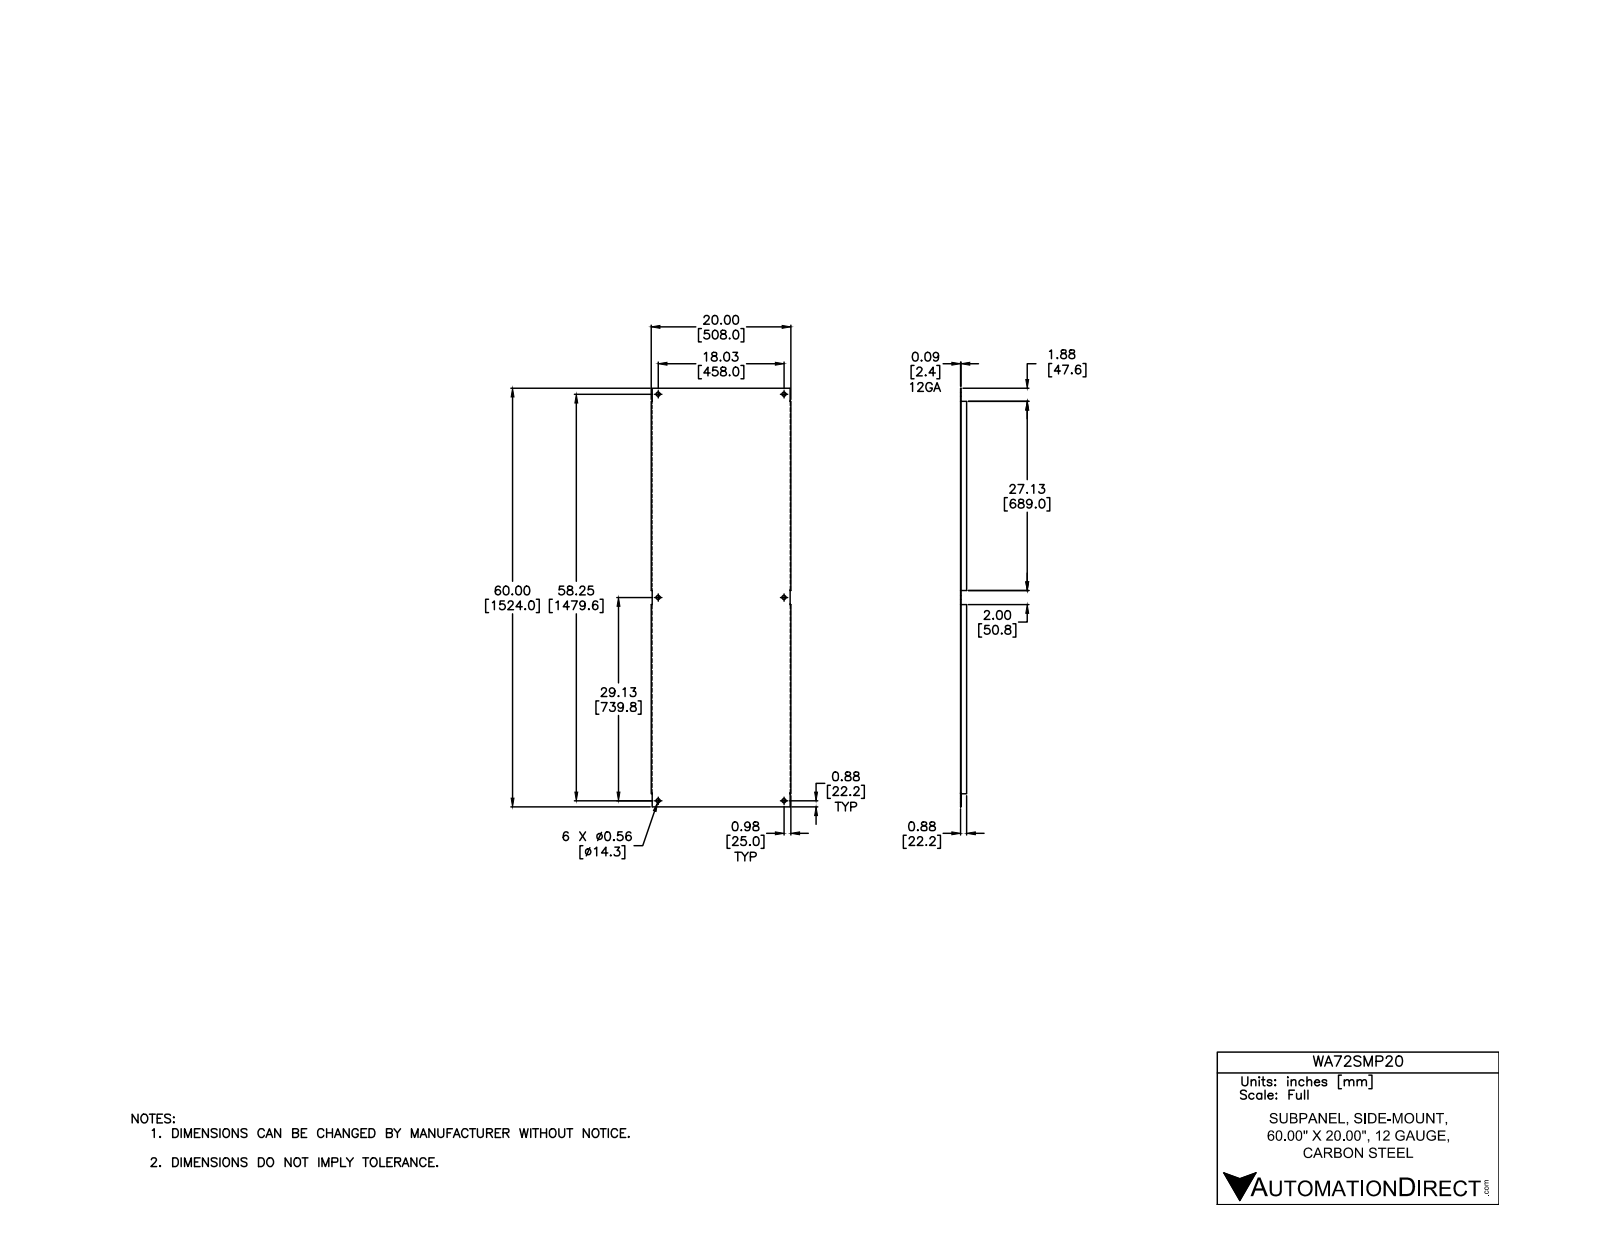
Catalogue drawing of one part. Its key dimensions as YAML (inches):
part_name: "WA60SMP14-WA90SMP20"
step_written_by: "Autodesk Inventor 2012 (AUTOMOTIVE_DESIGN)"
units: inches
bodies: {solids: 1, faces: 48, planar: 34, cylindrical: 14, other: 0}
overall_size: [60, 20, 0.875]
volume: 119.9
surface_area: 2575
round_holes:
  - {diameter: 0.563, count: 6}
partial_cylinders:
  - {radius: 0.015, count: 2}
  - {radius: 0.109, count: 2}
face_to_face_distances: [0.094, 19.906, 19.813, 20, 0.781, 0.875, 60, 0.109, 19.891, 0.015]
hole_center_spacings: [29.125, 34.256, 18.032, 58.25, 60.978]
